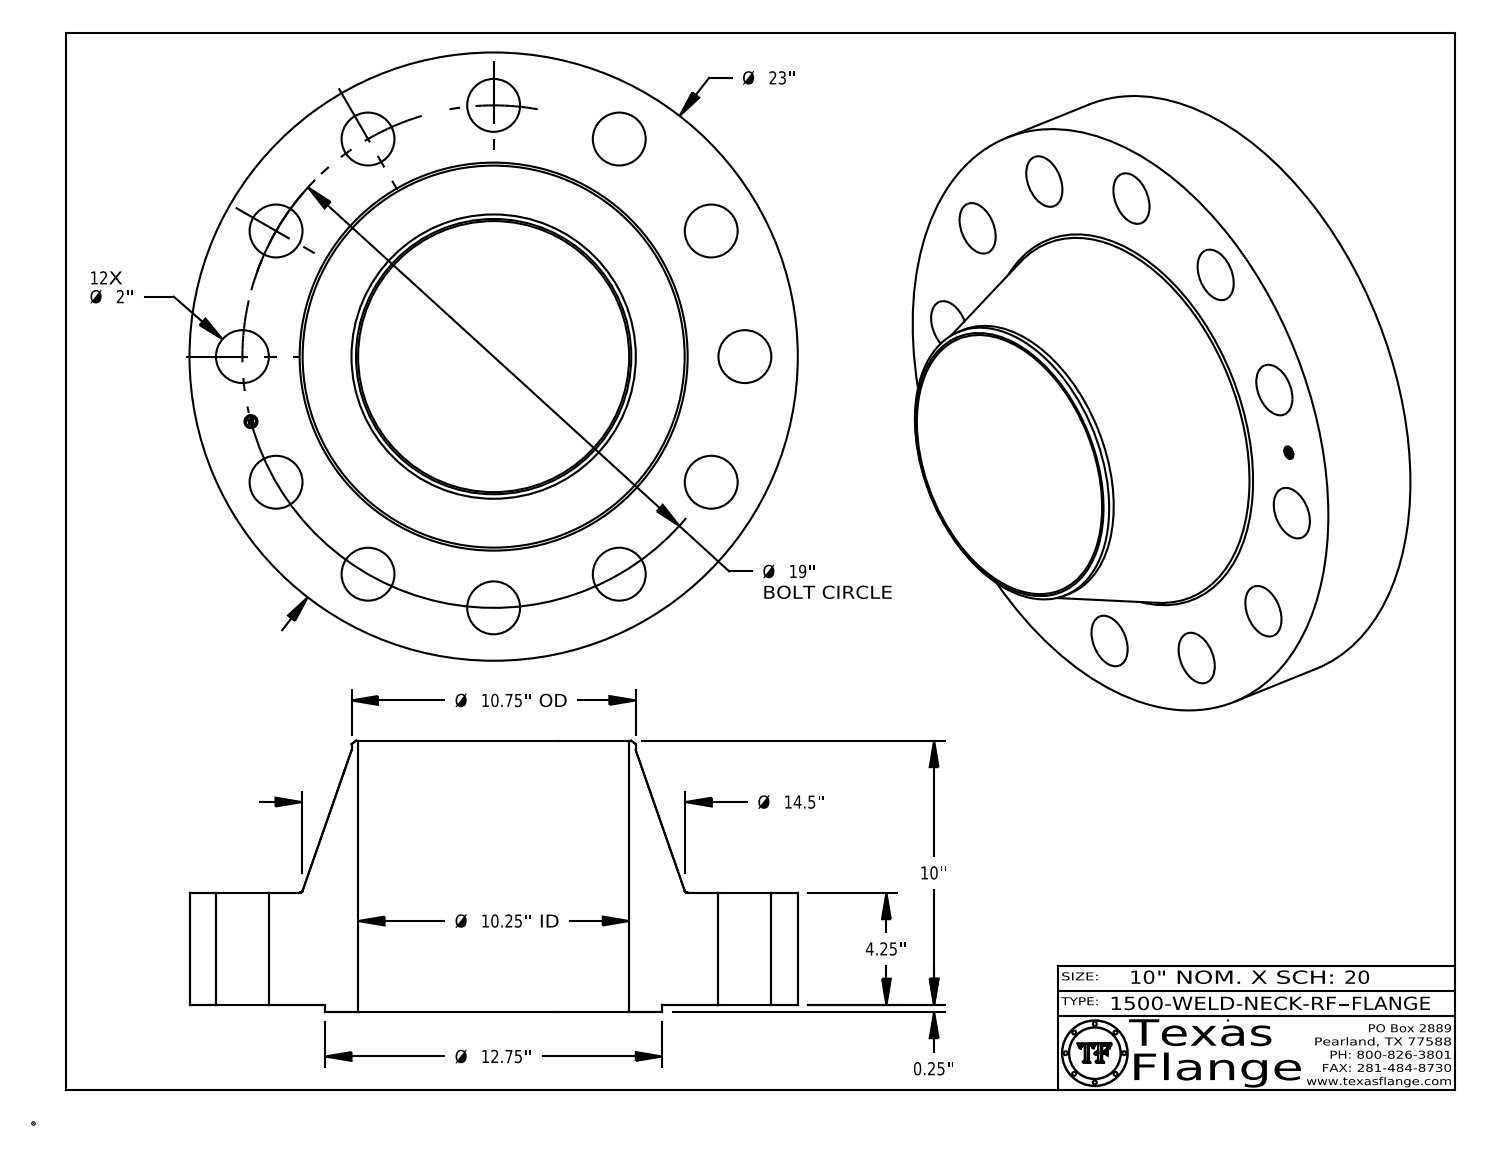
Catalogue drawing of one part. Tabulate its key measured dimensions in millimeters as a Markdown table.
| quantity | value |
| --- | --- |
| part name | 1500-WELD-NECK-RF |
| STEP written by | CATIA V5 STEP AP214 (AUTOMOTIVE_DESIGN) |
| units | millimeters |
| bodies | 1 solid, 427 faces (369 planar, 52 cylindrical, 6 other) |
| overall size | 584.2 × 584.2 × 260.4 |
| volume | 24 630 000 mm³ |
| surface area | 1 108 000 mm² |
| round holes (diameter × count) | 50.8 × 12, 12.6 × 1, 260.4 × 1 |
| round bosses / shafts (diameter × count) | 0.8 × 8, 584.2 × 1, 323.9 × 1, 273.1 × 1, 9.9 × 1 |
| main face-to-face distances | 108, 6.4, 114.3, 260.4, 254, 146.1, 113.9, 107.6, 0.4, 146.4 |
| hole center spacings | 241.3, 341.2, 417.9, 466.1, 124.9, 482.6, 124.9, 382.9 |
